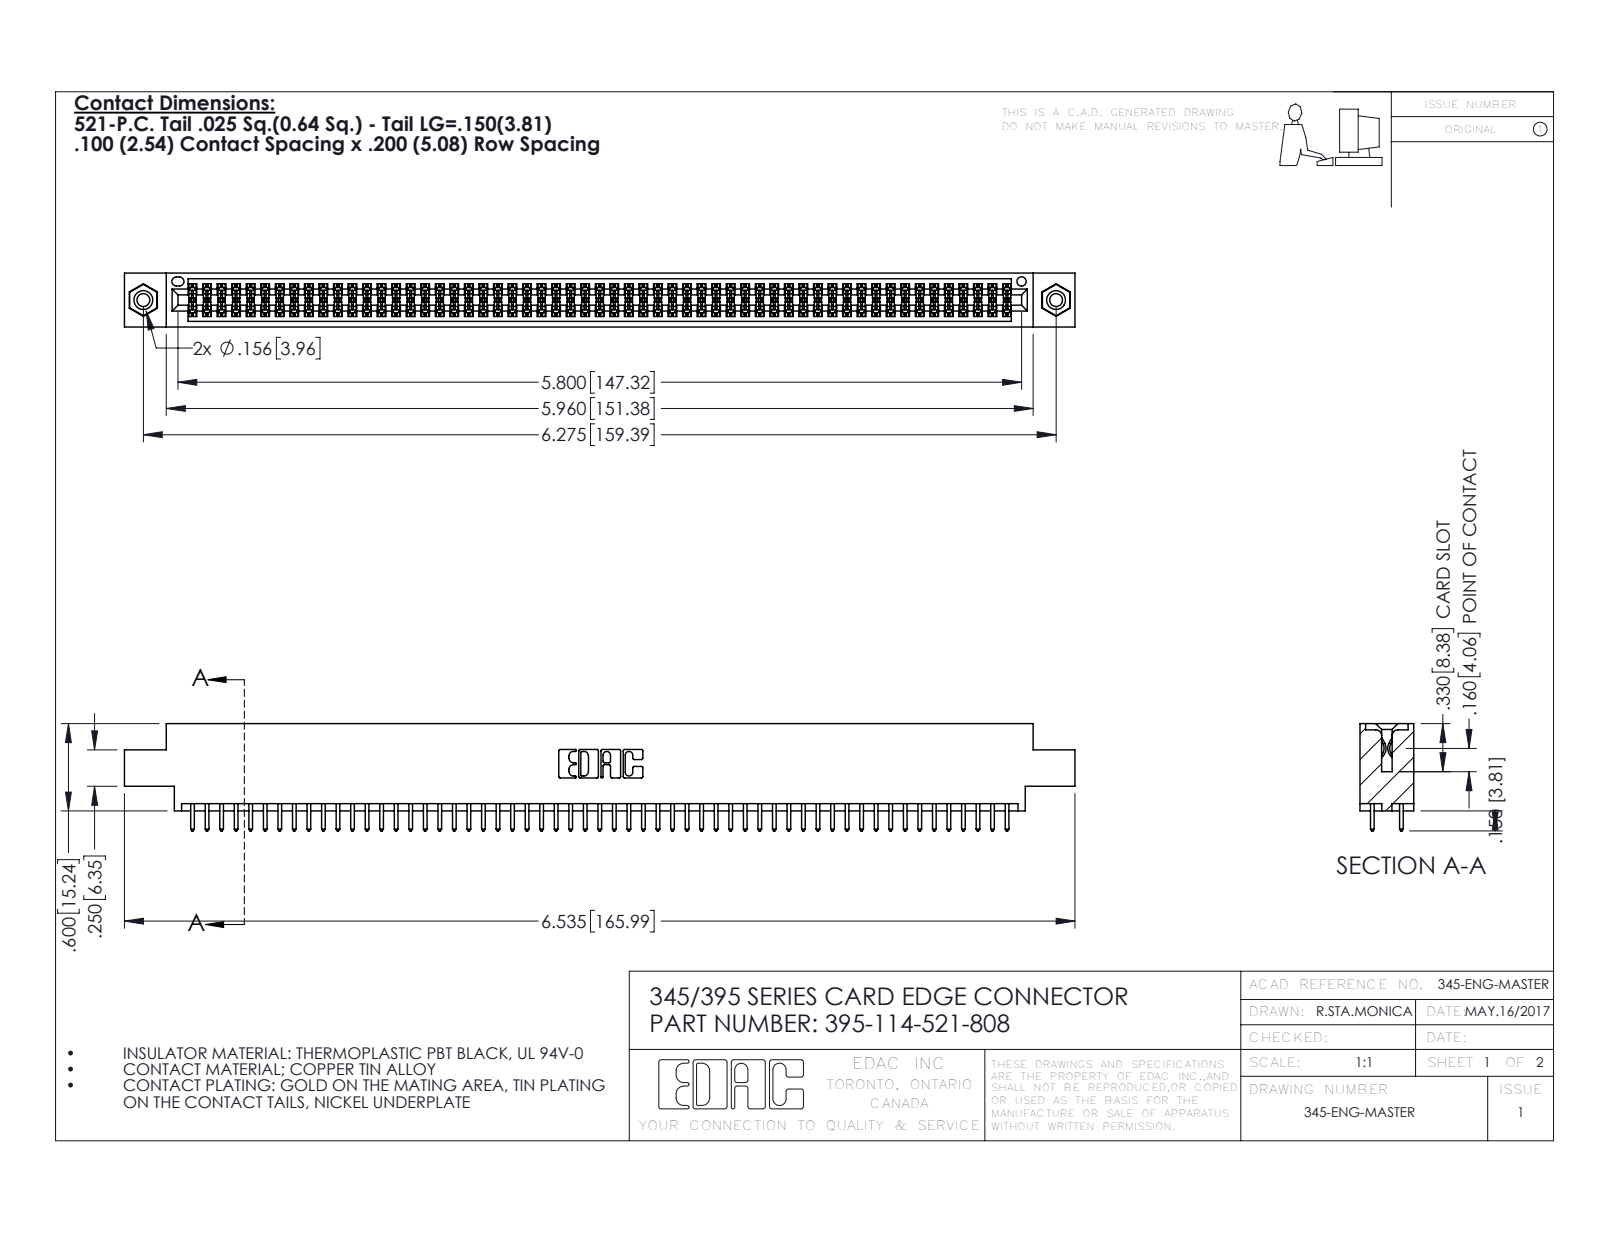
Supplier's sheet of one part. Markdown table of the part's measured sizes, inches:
| quantity | value |
| --- | --- |
| part name | 345-250-001_345-250-003-102; 395-114-521-808; 345 Part_0.170 Offset - 0.156 Dia-TI; 345-292-001_345-293-121 |
| STEP written by | SolidWorks 2016 (CONFIG_CONTROL_DESIGN) |
| units | inches |
| bodies | 117 solids, 5890 faces (3878 planar, 1996 cylindrical, 16 other) |
| overall size | 6.535 × 0.737 × 0.37 |
| volume | 0.982 in³ |
| surface area | 37.11 in² |
| round holes (diameter × count) | 0.089 × 2, 0.125 × 2, 0.156 × 2, 0.064 × 1 |
| round bosses / shafts (diameter × count) | 0.155 × 2 |
| partial cylindrical surfaces (radius × count) | 0.006 × 171, 0.01 × 114, 0.01 × 22, 0.007 × 6, 0.031 × 6, 0.026 × 3, 0.014 × 2, 0.019 × 2 |
| main face-to-face distances | 0.072, 0.298, 0.2, 0.37, 0.098, 0.272, 0.025, 0.225, 0.175, 0.149 |
| hole center spacings | 0.27, 6.039, 6.275 |
